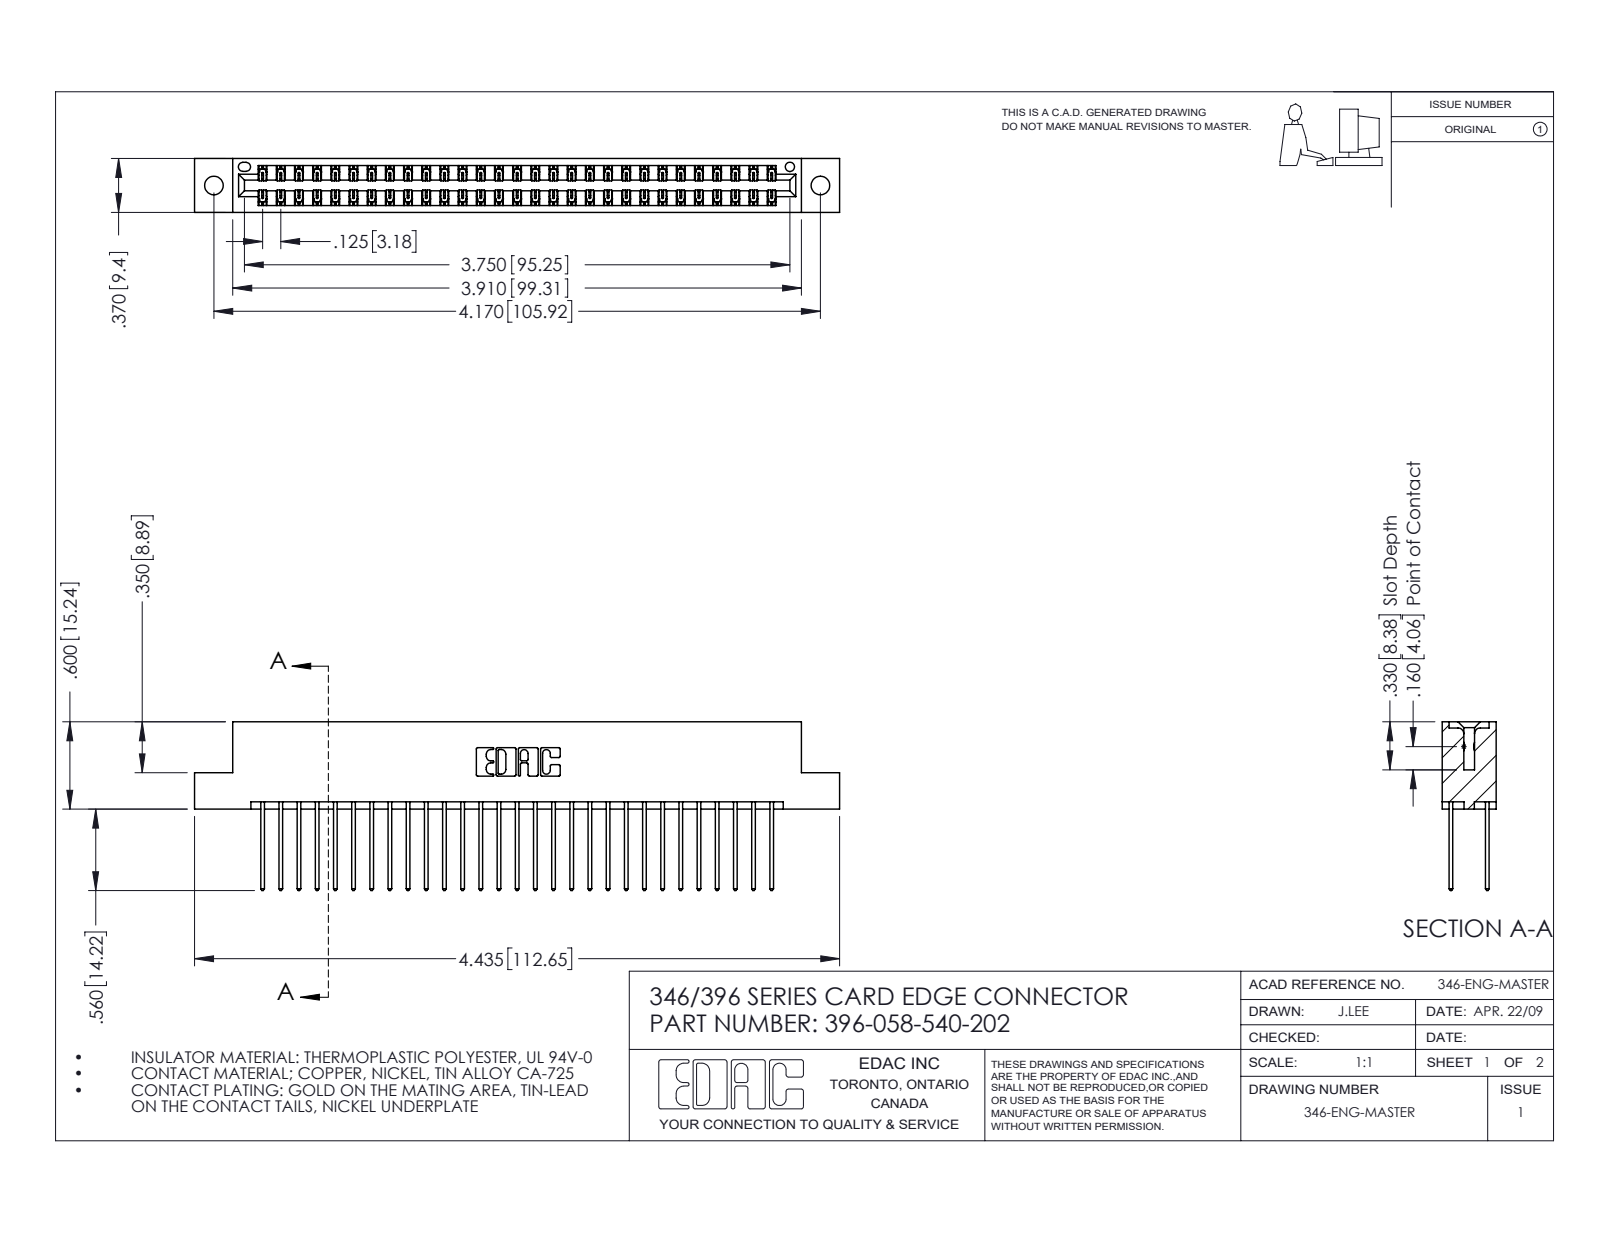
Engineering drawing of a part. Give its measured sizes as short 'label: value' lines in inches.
name: 396-058-540-202; 346 Part_Flush Mounting Lugs - 0.128 Dia; 345-292-001_345-293-140
written by: SolidWorks 2016 (CONFIG_CONTROL_DESIGN)
unit: in
bodies: 59 solids, 3138 faces (2106 planar, 1032 cylindrical, 0 other)
size: 4.435 × 1.16 × 0.37
volume: 0.675 in³; area: 24.46 in²
holes: 2× ⌀0.128, 1× ⌀0.064
rounds: 87× R0.006, 58× R0.01, 22× R0.01, 6× R0.007, 6× R0.031, 3× R0.026, 2× R0.014, 2× R0.022
face distances: 0.048, 0.322, 0.25, 0.072, 0.298, 0.025, 0.37, 0.275, 0.148, 0.222
hole spacings: 0.246, 3.962, 4.17
